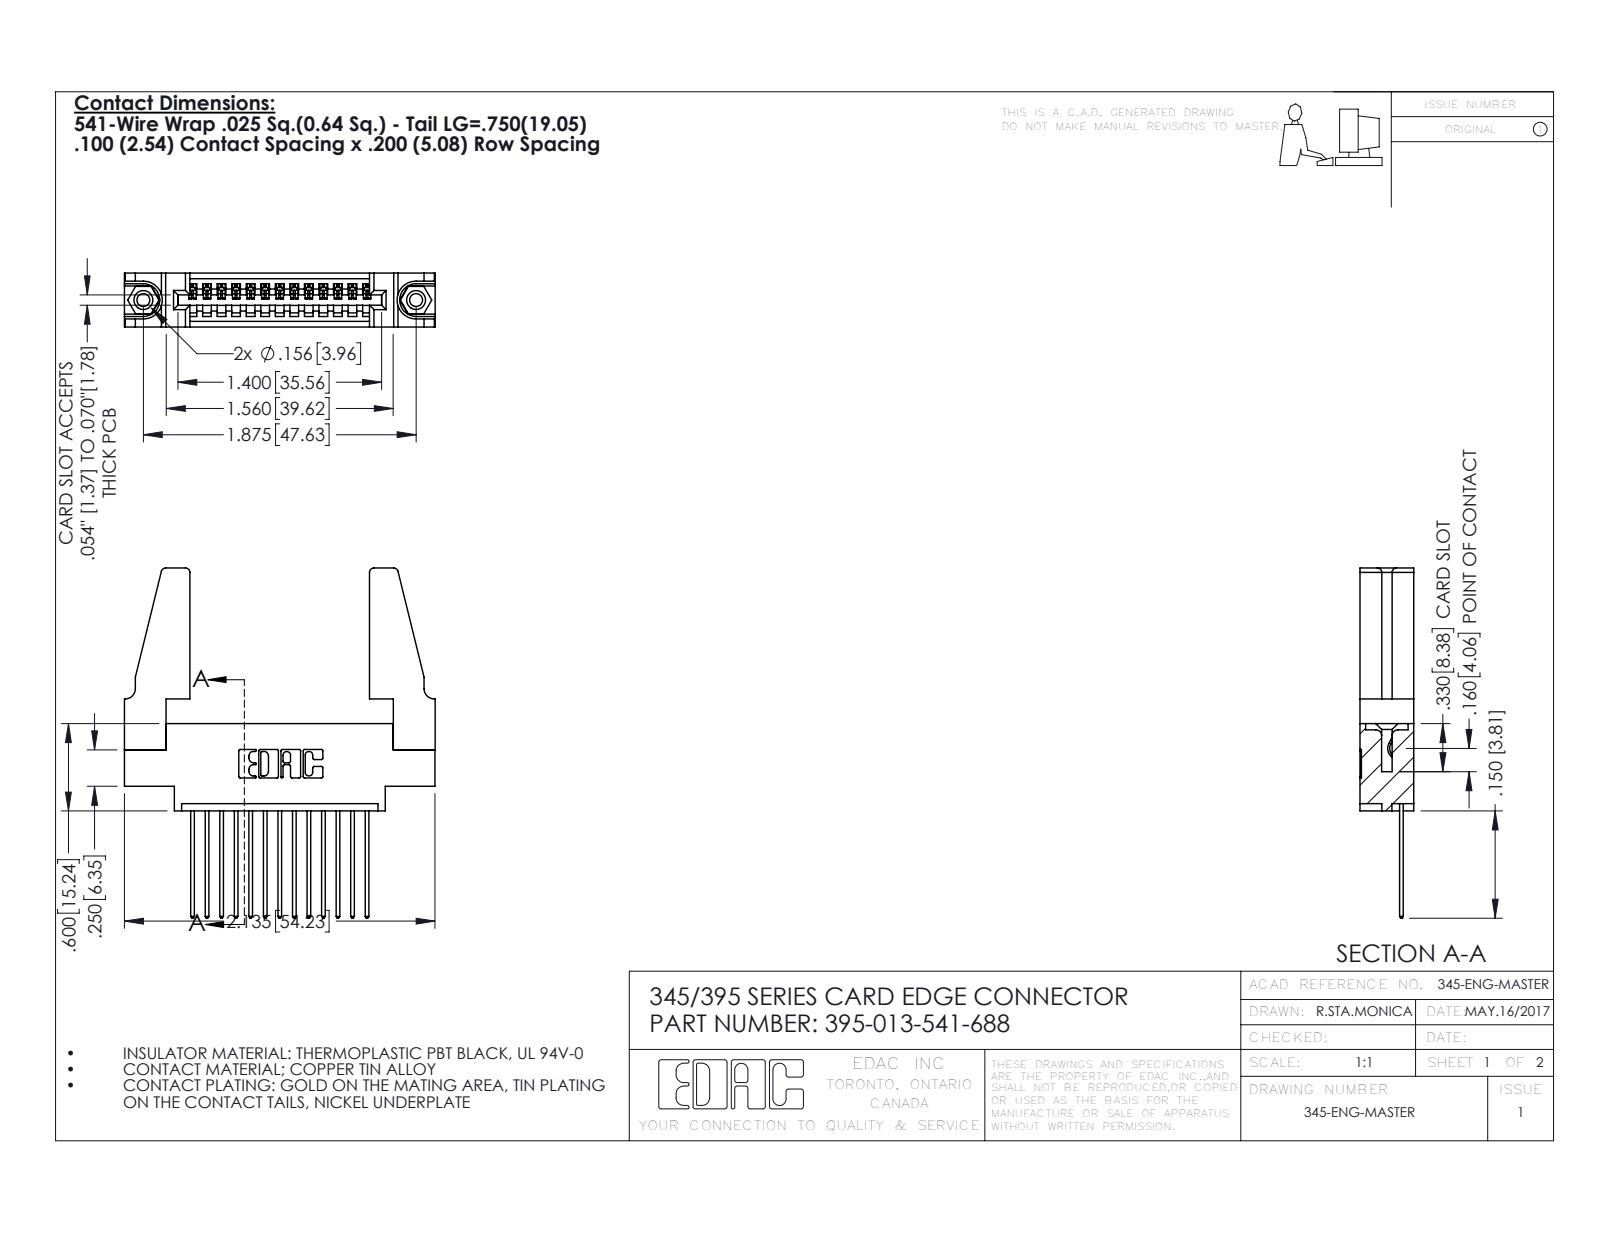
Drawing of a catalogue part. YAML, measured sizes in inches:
part_name: "345-250-001_345-250-001-102; 395-013-541-688; 345 Part_0.170 Offset - 0.156 Dia-TH; 345-220-078_345-220-088 (+1 more)"
step_written_by: "SolidWorks 2016 (CONFIG_CONTROL_DESIGN)"
units: inches
bodies: {solids: 18, faces: 1008, planar: 676, cylindrical: 316, other: 16}
overall_size: [2.407, 2.136, 0.37]
volume: 0.494
surface_area: 14.81
round_holes:
  - {diameter: 0.089, count: 2}
  - {diameter: 0.125, count: 2}
  - {diameter: 0.156, count: 2}
  - {diameter: 0.064, count: 1}
round_bosses_or_shafts:
  - {diameter: 0.155, count: 2}
partial_cylinders:
  - {radius: 0.006, count: 26}
  - {radius: 0.01, count: 26}
  - {radius: 0.01, count: 22}
  - {radius: 0.03, count: 8}
  - {radius: 0.007, count: 6}
  - {radius: 0.031, count: 6}
  - {radius: 0.026, count: 3}
  - {radius: 0.031, count: 2}
face_to_face_distances: [0.37, 0.072, 0.298, 0.098, 0.272, 0.025, 0.2, 0.225, 0.148, 0.15]
hole_center_spacings: [0.27, 1.643, 1.875]
